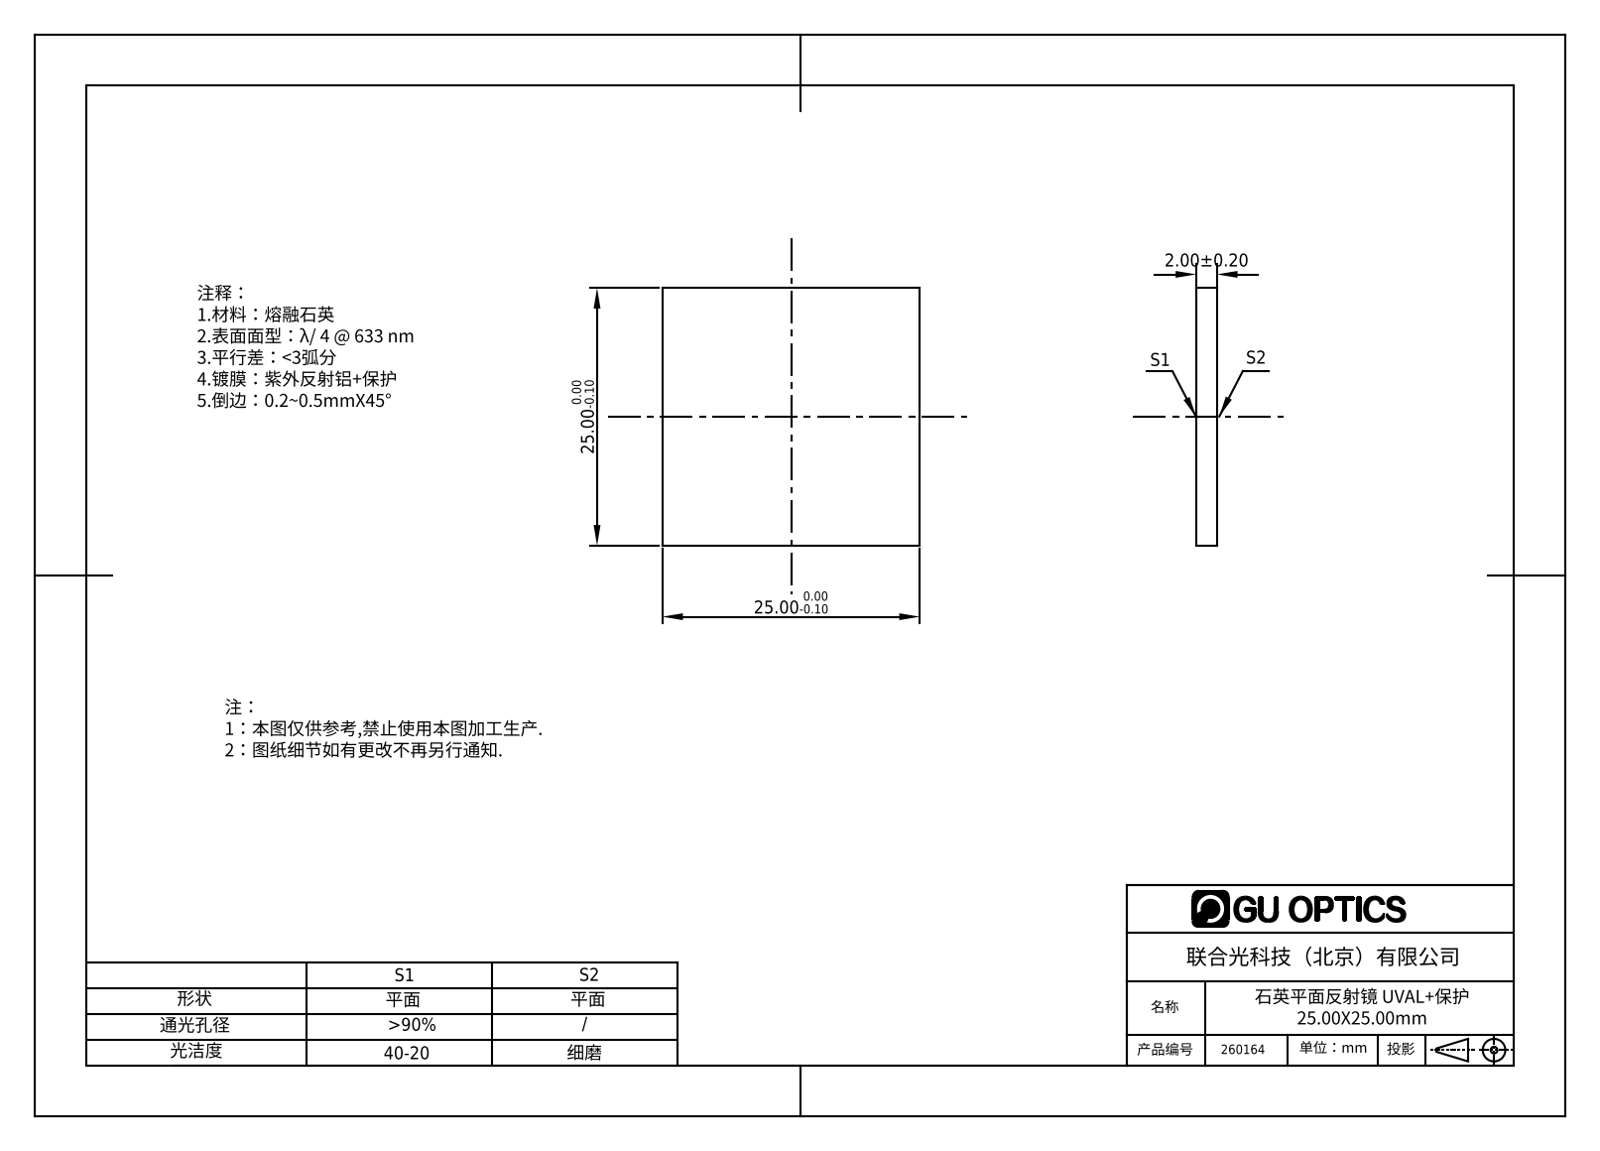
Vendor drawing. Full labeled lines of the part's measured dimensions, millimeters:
Part name (STEP PRODUCT): 260008
STEP written by: SolidWorks 2016 (AUTOMOTIVE_DESIGN)
Units: millimetres
Bodies: 1 solid, 6 faces (6 planar, 0 cylindrical, 0 other)
Overall size (bounding box): 25 × 25 × 2
Volume: 1 250 mm³ · Surface area: 1 450 mm²
Main face-to-face distances: 2, 25
